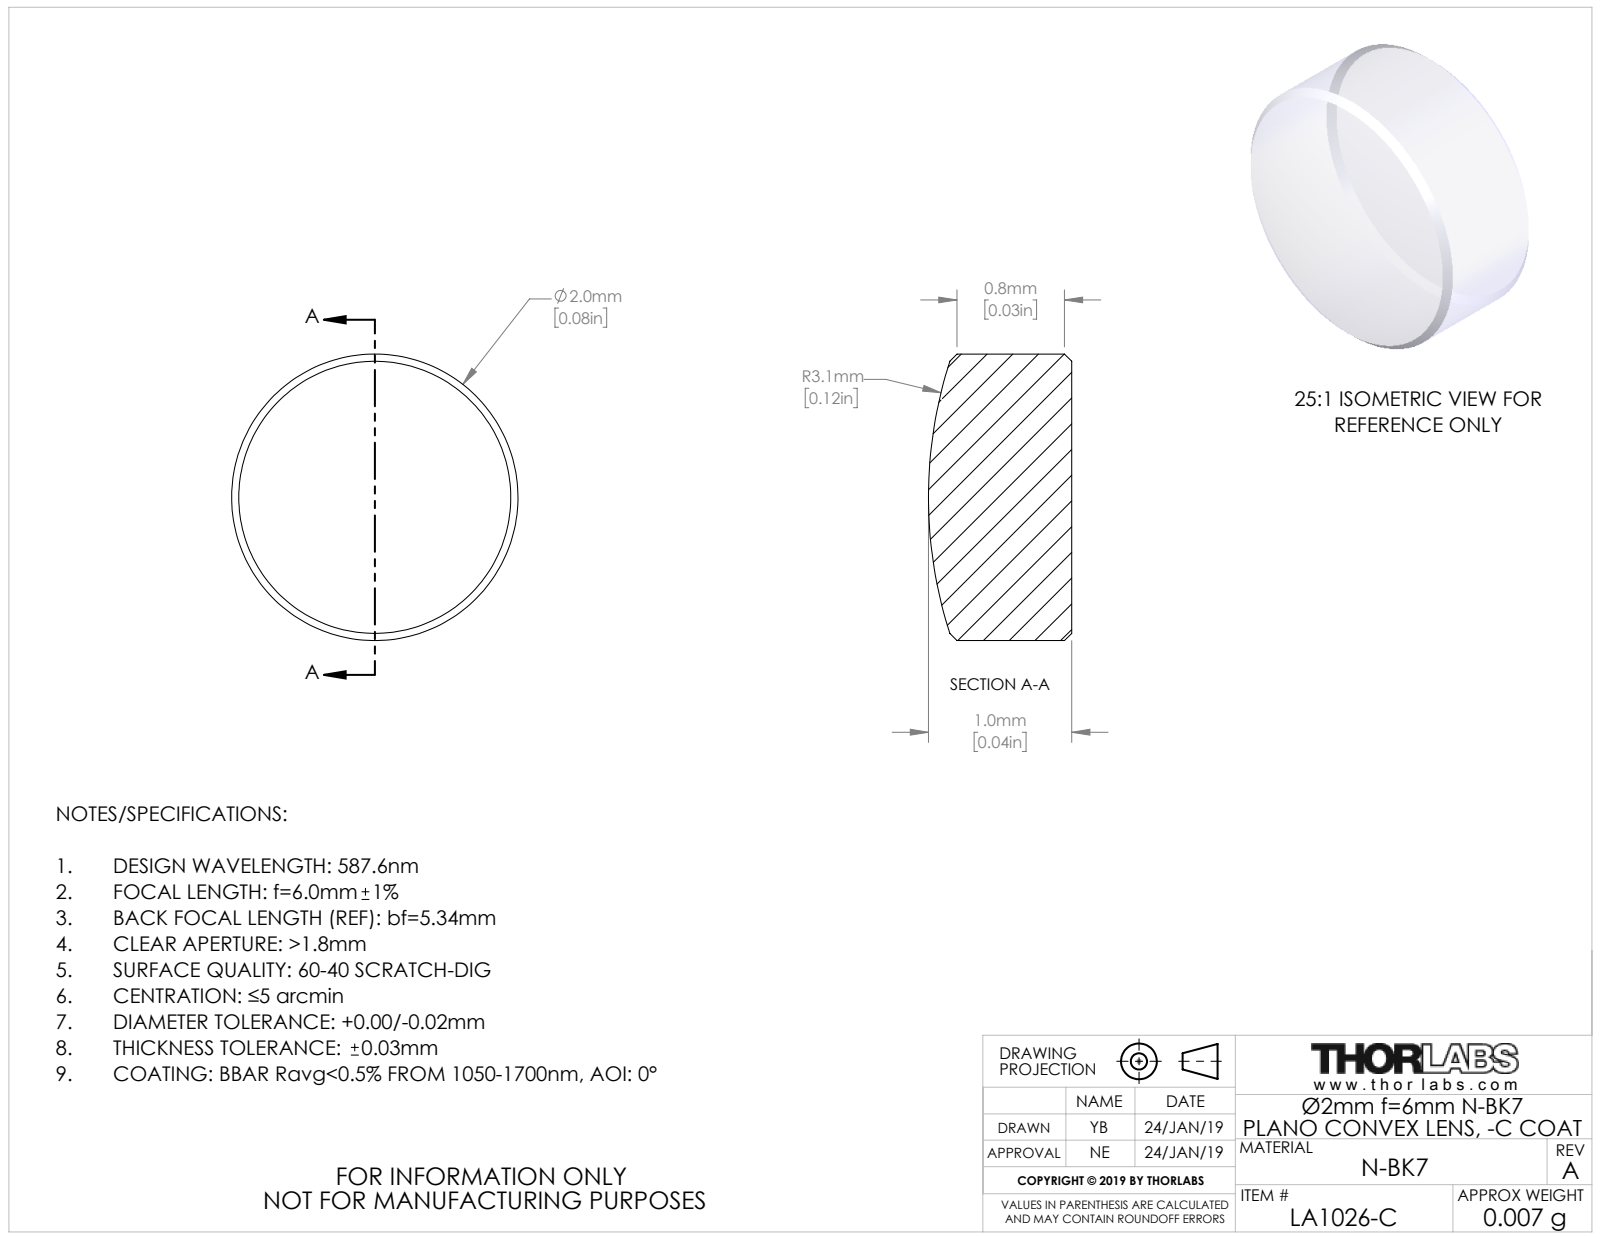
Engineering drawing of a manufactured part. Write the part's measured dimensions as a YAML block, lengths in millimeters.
part_name: "TTN162613-E0W"
step_written_by: "SolidWorks 2018 (CONFIG_CONTROL_DESIGN)"
units: millimeters
bodies: {solids: 1, faces: 9, planar: 1, cylindrical: 2, other: 6}
overall_size: [2, 2, 1]
volume: 3
surface_area: 11
round_bosses_or_shafts:
  - {diameter: 2, count: 1}
